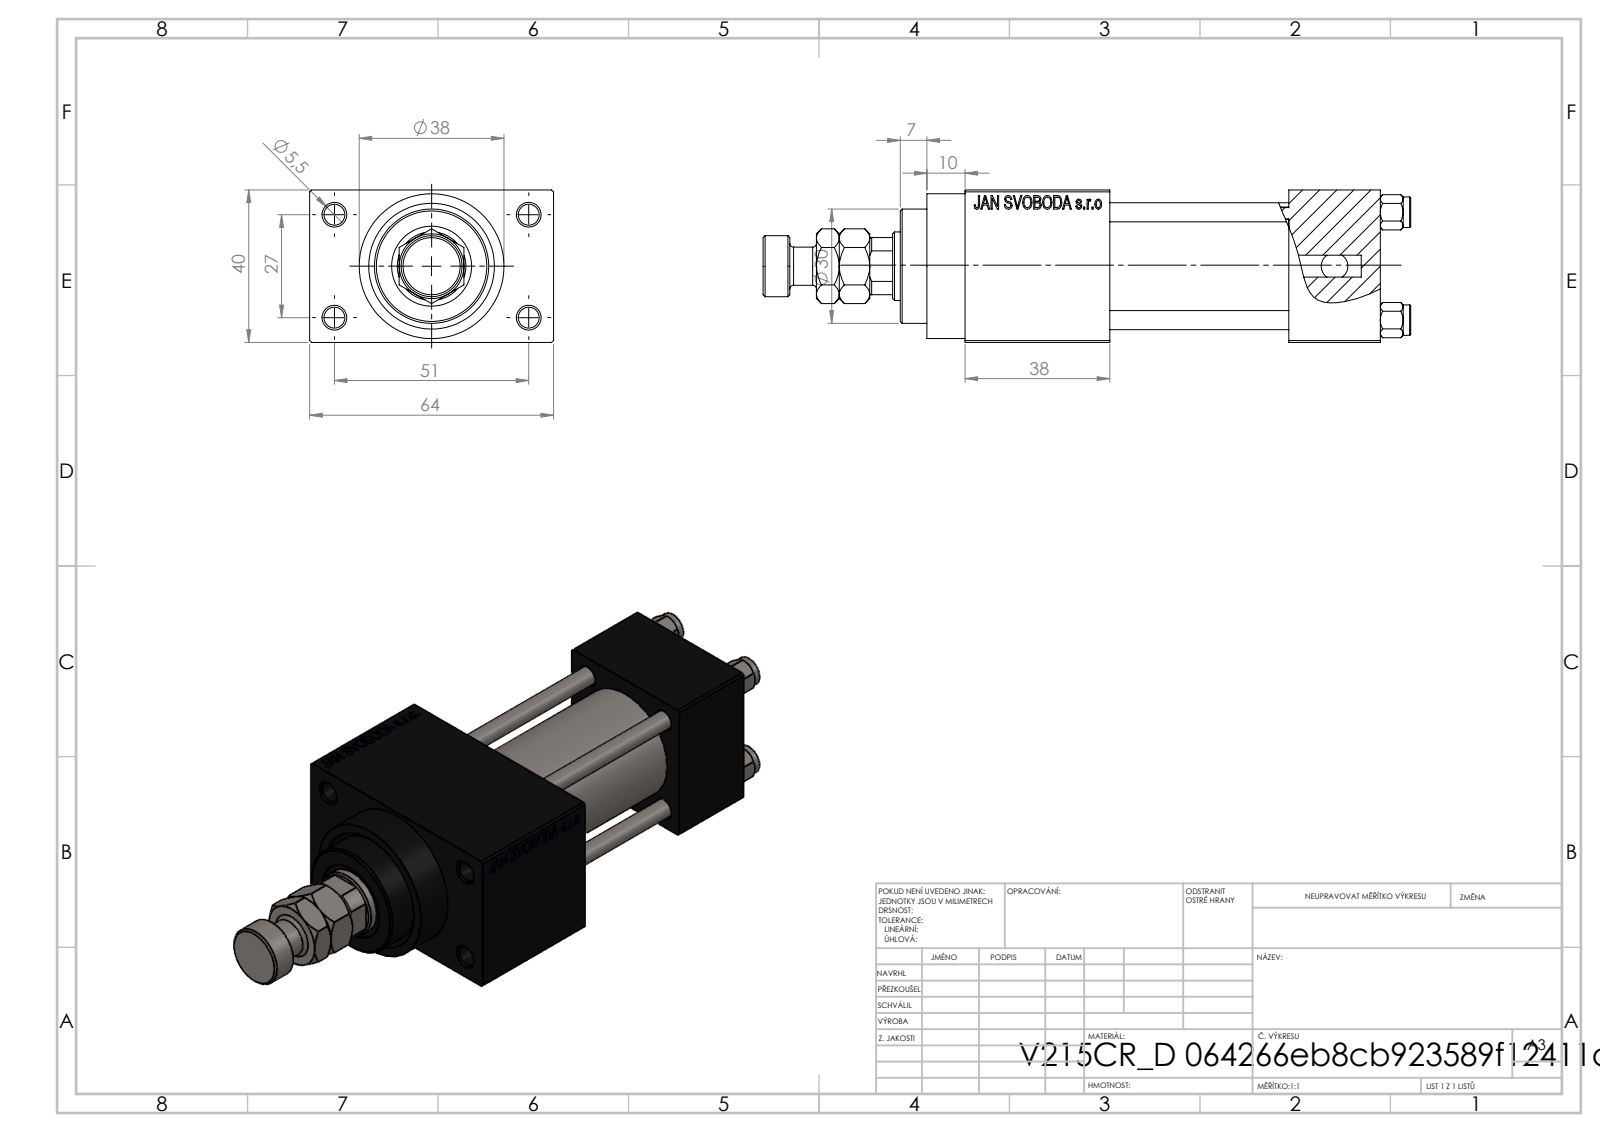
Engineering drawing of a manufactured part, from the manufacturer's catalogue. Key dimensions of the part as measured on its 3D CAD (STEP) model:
Part name (STEP PRODUCT): V215CR_D_TYCINKA; V215CR_D_Body; NUT_M5_D; V215_VC_A (+2 more)
STEP written by: SolidWorks 2019 (CONFIG_CONTROL_DESIGN)
Units: millimetres
Bodies: 12 solids, 1153 faces (511 planar, 90 cylindrical, 552 other)
Overall size (bounding box): 170 × 64 × 40
Volume: 184 548 mm³ · Surface area: 66 694 mm²
Round holes (diameter × count): ⌀5 ×4, ⌀5.5 ×4, ⌀20 ×3, ⌀7 ×2, ⌀13.16 ×2, ⌀8.5 ×1, ⌀18 ×1, ⌀21 ×1, ⌀25 ×1, ⌀30 ×1
Round bosses / shafts (diameter × count): ⌀8 ×4, ⌀38 ×1, ⌀31 ×1, ⌀16 ×1, ⌀10 ×1
Partial cylindrical surfaces — rounded edges, fillets, slot ends (radius × count): R8.5 ×1
Main face-to-face distances: 40, 12, 47, 24, 71, 52, 38, 109, 85, 64
Hole centre spacings: 11.37, 20.01, 28.3, 28.85, 29.89, 39.66, 48.34, 27
